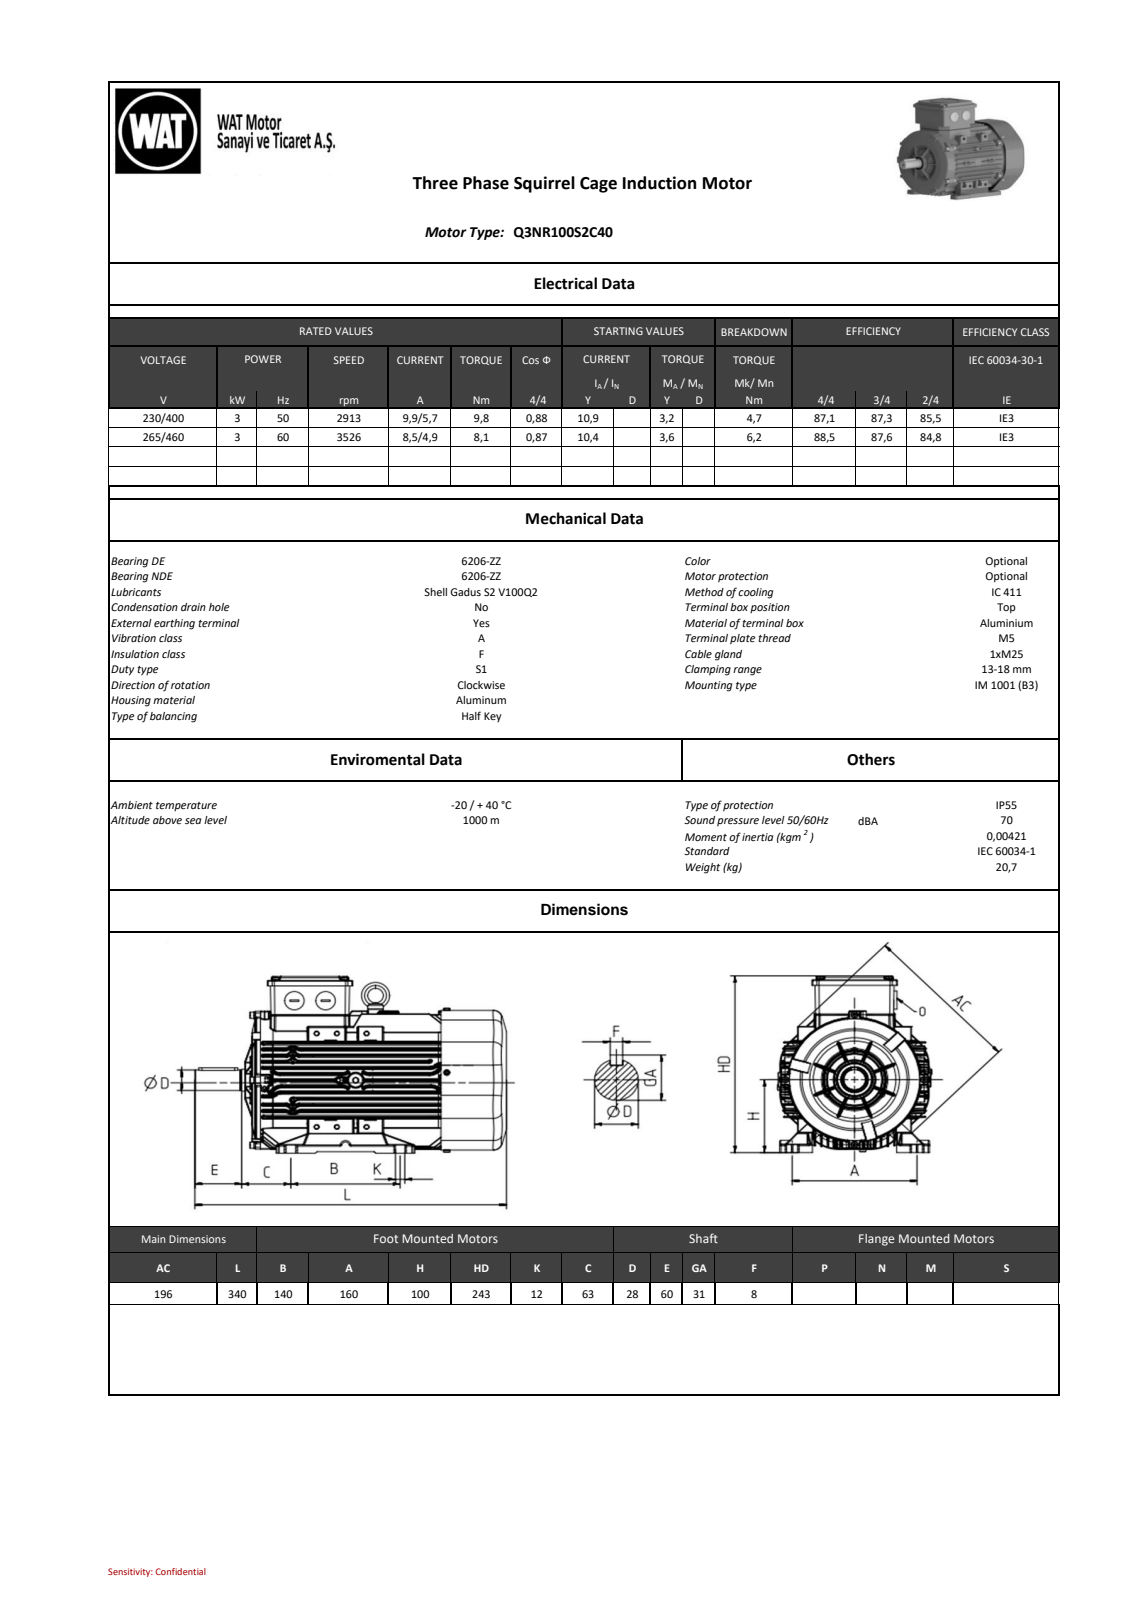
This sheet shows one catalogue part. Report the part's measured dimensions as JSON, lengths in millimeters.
{"part_name": "C90127E0127Fj67r", "step_written_by": "SIEMENS PLM Software NX 11.0 (AUTOMOTIVE_DESIGN)", "units": "millimeters", "bodies": {"solids": 0, "faces": 14488, "planar": 2914, "cylindrical": 4381, "other": 7193}, "overall_size": [340, 230.5, 200], "round_holes": [[5, 6], [6.5, 6], [2, 2], [2.5, 2], [3, 2], [12, 2], [25, 2], [4, 1], [8.5, 1], [10.5, 1], [28.6, 1], [32.94, 1]], "round_bosses_or_shafts": [[8, 7], [4, 7], [11.8, 6], [10, 6], [6, 6], [35, 2], [27.8, 2], [25.25, 2]], "partial_cylinders_radius": [[0.5, 1252], [0.75, 576], [0.8, 523], [1, 316], [0.25, 144], [4, 102], [2, 89], [1.5, 72]], "face_to_face_distances": [0.8, 2, 14, 41, 269, 40.2, 268.2, 228, 5.28, 28], "hole_center_spacings": [92, 39, 96.14, 156.89, 184, 12.13, 14.13, 17.07]}
